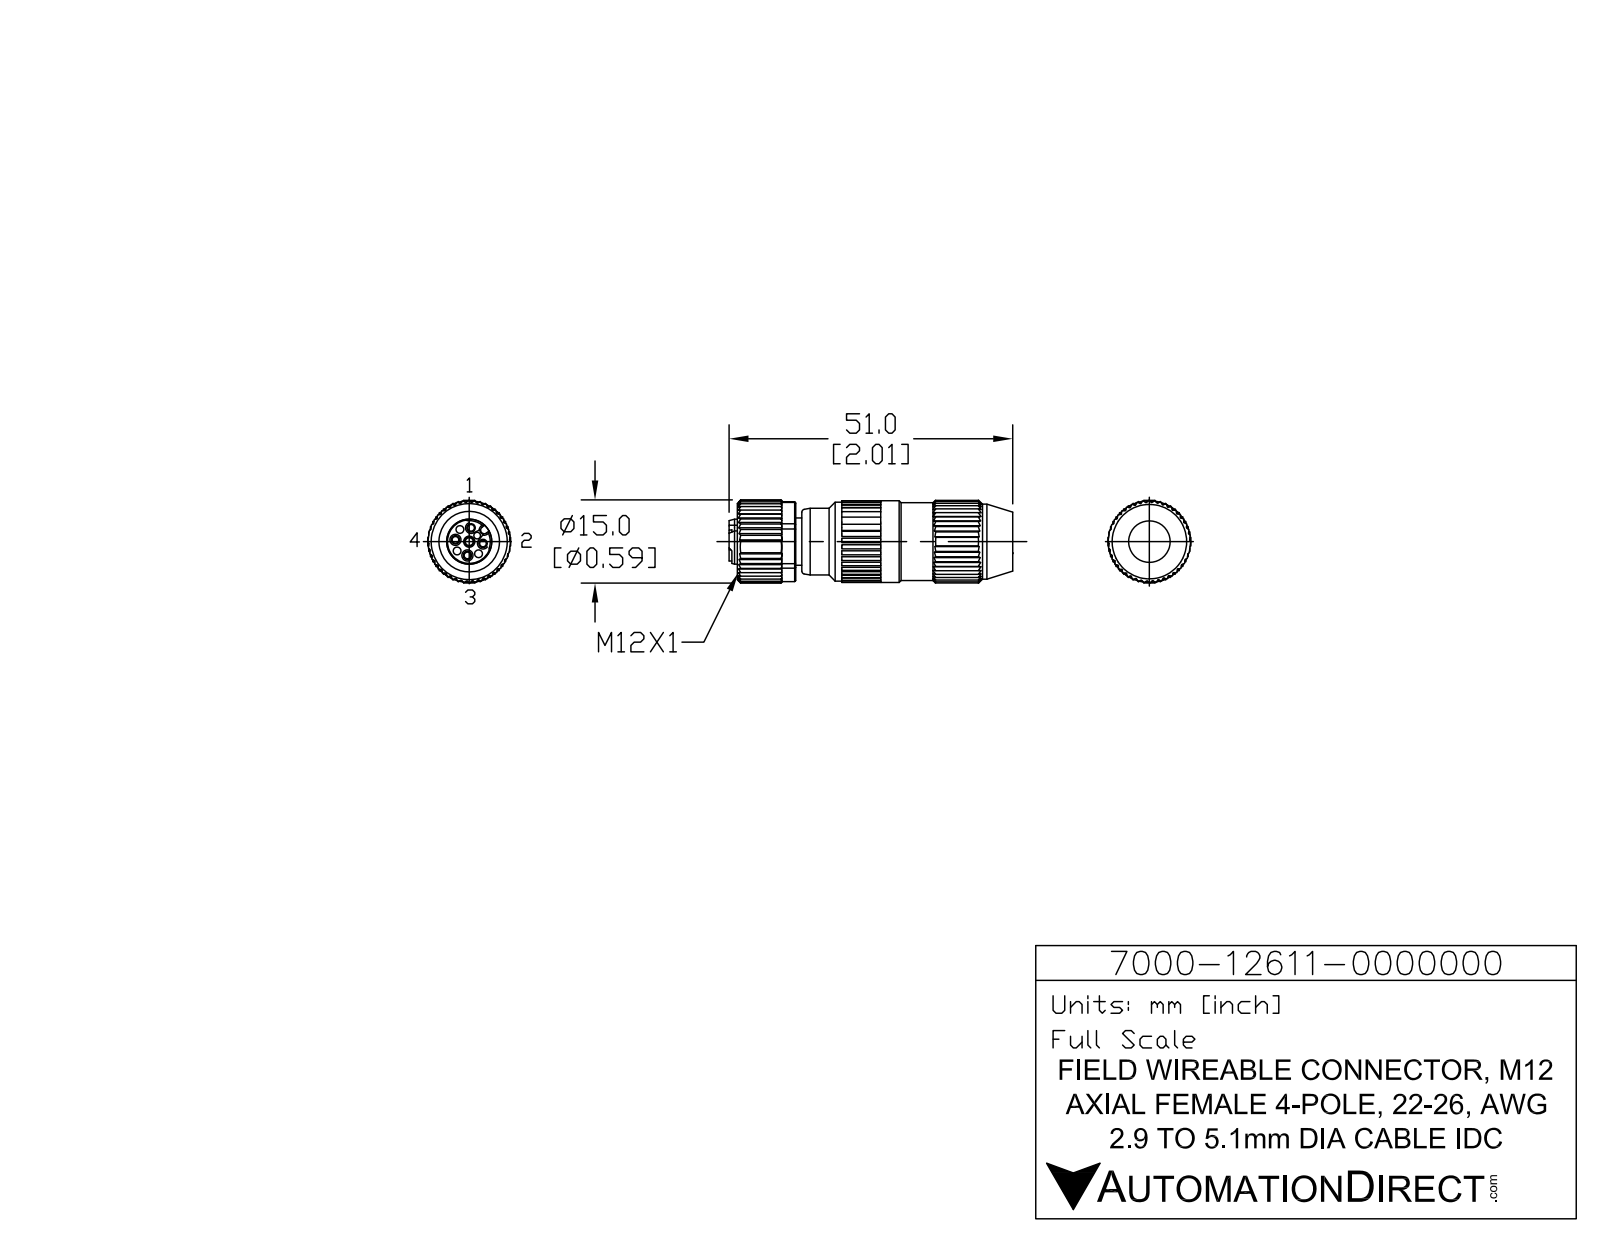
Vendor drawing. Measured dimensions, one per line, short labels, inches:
name: 7000-12611-0000000
written by: SolidWorks 2015 (AUTOMOTIVE_DESIGN)
unit: in
bodies: 1 solid, 565 faces (369 planar, 129 cylindrical, 67 other)
size: 44 × 15 × 15
volume: 5 830 in³; area: 3 784 in²
holes: 5× ⌀1, 1× ⌀6.1, 1× ⌀11
bosses: 1× ⌀15, 1× ⌀13.827, 1× ⌀13.6, 1× ⌀9.047, 1× ⌀8.12
rounds: 1× R0.5, 1× R7.496
face distances: 2, 8.707, 8, 33.46, 9.46, 32, 41.46, 2.54, 44, 12
hole spacings: 2.5, 3.535, 5
